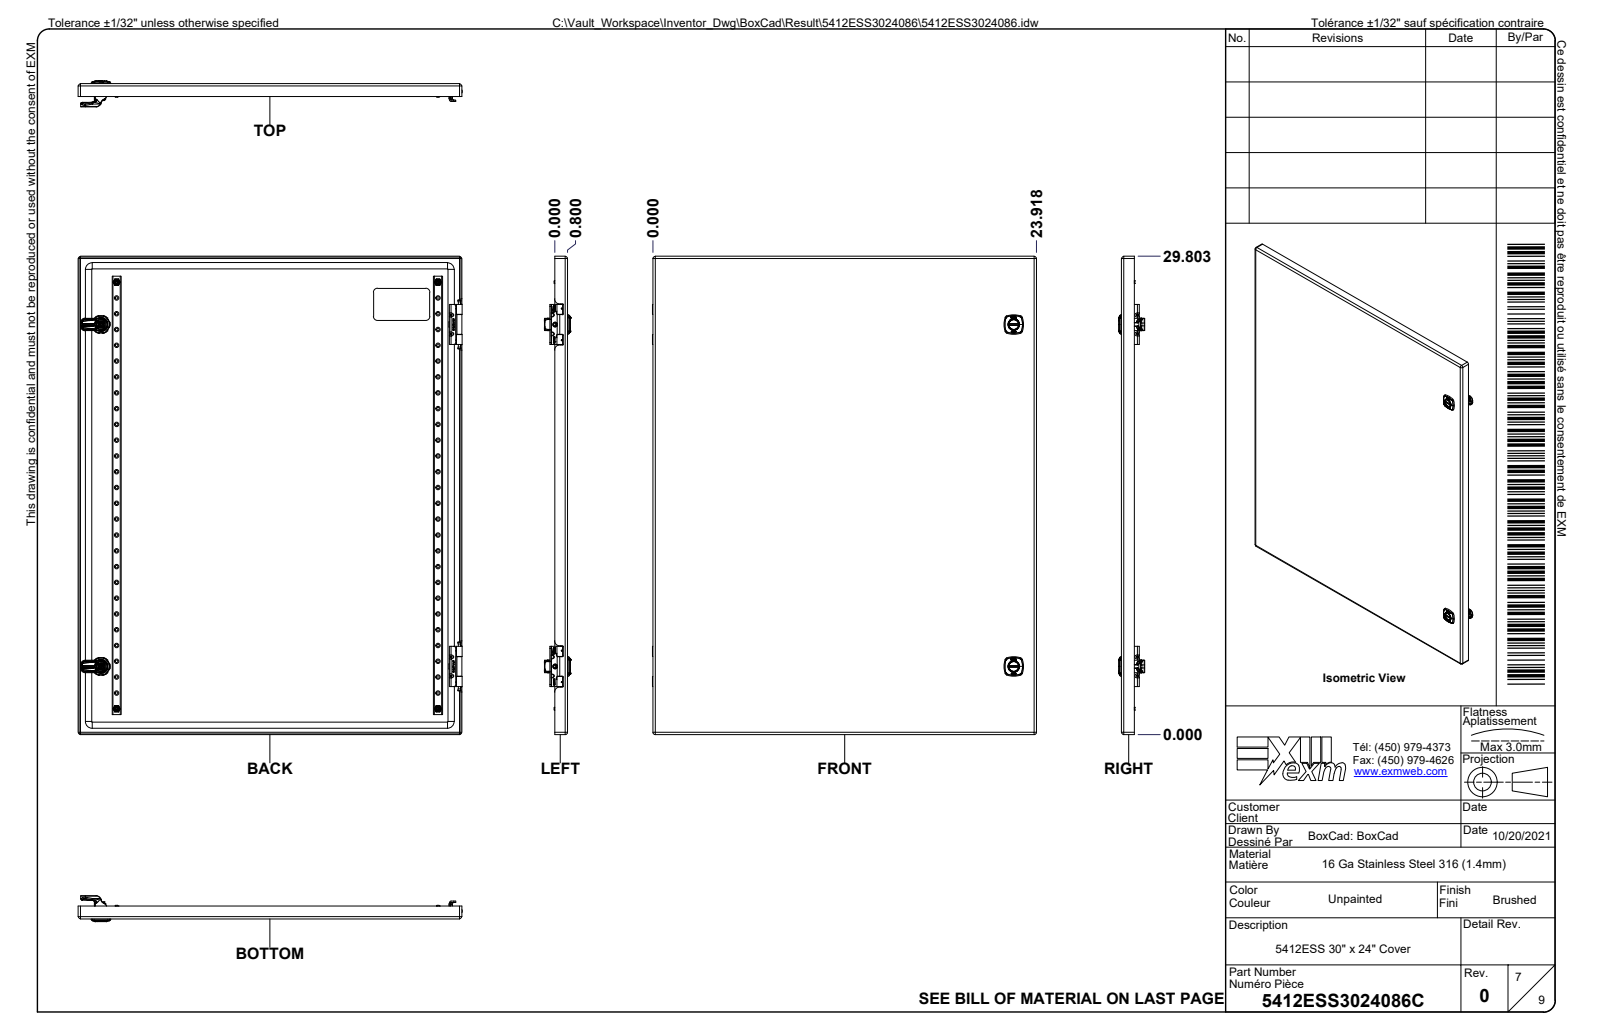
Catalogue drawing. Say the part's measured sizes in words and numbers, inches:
The part is named "5412ESS3024086; 5412ESS3024086B; 5412ESS3024086B-P; STK-Q-16020 (+8 more)". Its 3-D file was written by "Autodesk Inventor 2024 (AUTOMOTIVE_DESIGN)". It is 64 solids with 9386 faces: 3057 planar, 1991 cylindrical and 4338 other. Overall it measures 30 by 24 by 9.306 inches. Its volume is 219.5 cubic inches and its surface area 6 856 square inches. Round holes: 52 of diameter 0.165, 9 of diameter 0.03, 8 of diameter 0.201, 8 of diameter 0.315, 6 of diameter 0.29, 6 of diameter 0.311, 4 of diameter 0.044, 4 of diameter 0.197, 4 of diameter 0.268, 4 of diameter 0.27, 4 of diameter 0.39, 2 of diameter 0.236. Round bosses or shafts: 52 of diameter 0.237, 9 of diameter 0.232, 9 of diameter 0.03, 8 of diameter 0.039, 4 of diameter 0.717, 4 of diameter 0.374, 4 of diameter 0.311, 4 of diameter 0.262. Partial cylindrical surfaces (rounded edges, fillets, slot ends): 106 of radius 0.02, 68 of radius 0.008, 66 of radius 0.039, 34 of radius 0.012, 34 of radius 0.031, 28 of radius 0.01, 24 of radius 0.084, 20 of radius 0.125. The main face-to-face distances are 0.053, 9.082, 9.029, 9.135, 0.927, 0.874, 8.155, 8.208, 0.105, 1.032. The hole center spacings are 0.984, 1.969, 2.953, 3.937, 4.921, 5.906, 6.89, 7.874.
